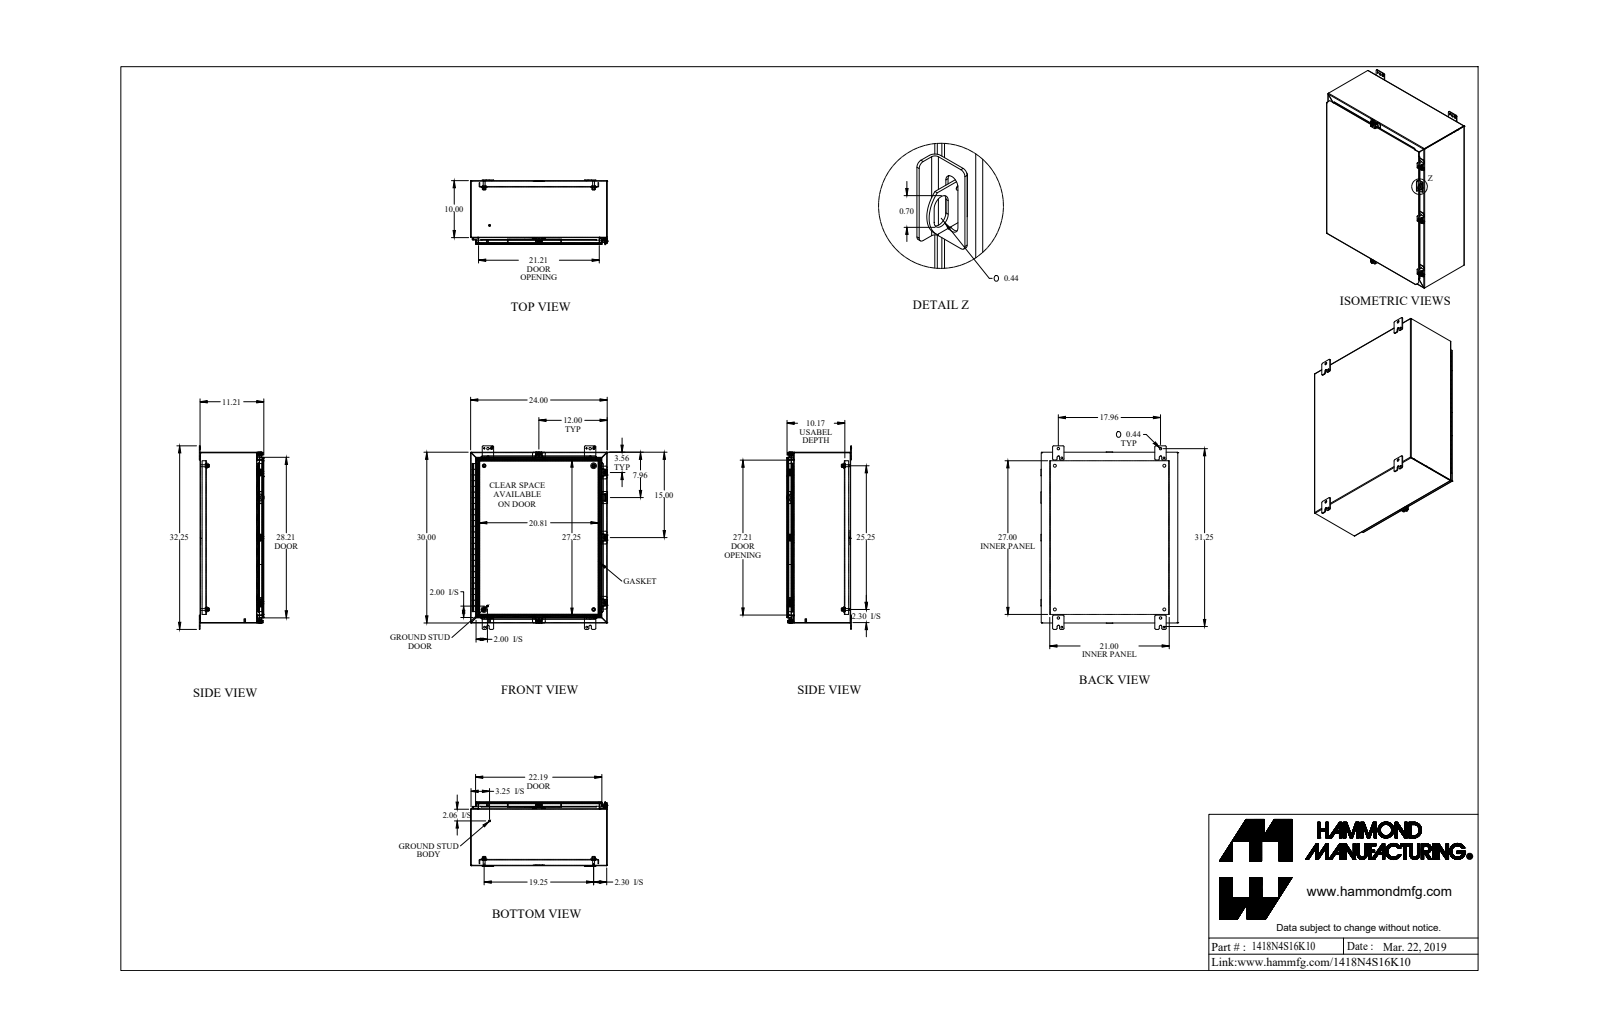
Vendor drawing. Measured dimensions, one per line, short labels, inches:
name: 1418N4S16K10_Default
written by: SolidWorks 2019 (CONFIG_CONTROL_DESIGN)
unit: in
bodies: 43 solids, 1538 faces (827 planar, 571 cylindrical, 140 other)
size: 32.25 × 24.063 × 11.375
volume: 273.1 in³; area: 7 190 in²
holes: 5× ⌀0.213, 5× ⌀0.265, 5× ⌀0.375, 4× ⌀0.313, 4× ⌀0.437, 4× ⌀0.5, 2× ⌀0.307, 2× ⌀0.445, 1× ⌀0.11, 1× ⌀0.125
bosses: 5× ⌀0.5, 5× ⌀0.39, 5× ⌀0.244, 4× ⌀0.65, 4× ⌀0.375, 4× ⌀0.332, 2× ⌀1, 2× ⌀0.313
rounds: 27× R0.048, 27× R0.143, 24× R0.036, 24× R0.108, 24× R0.25, 22× R0.188, 12× R0.125, 10× R0.141
face distances: 0.072, 0.072, 11.066, 11.138, 11.138, 11.21, 0.937, 0.095, 1.009, 23.928
hole spacings: 29.018, 9.857, 29.75, 3.065, 9.857, 12.803, 19.25, 24.157
